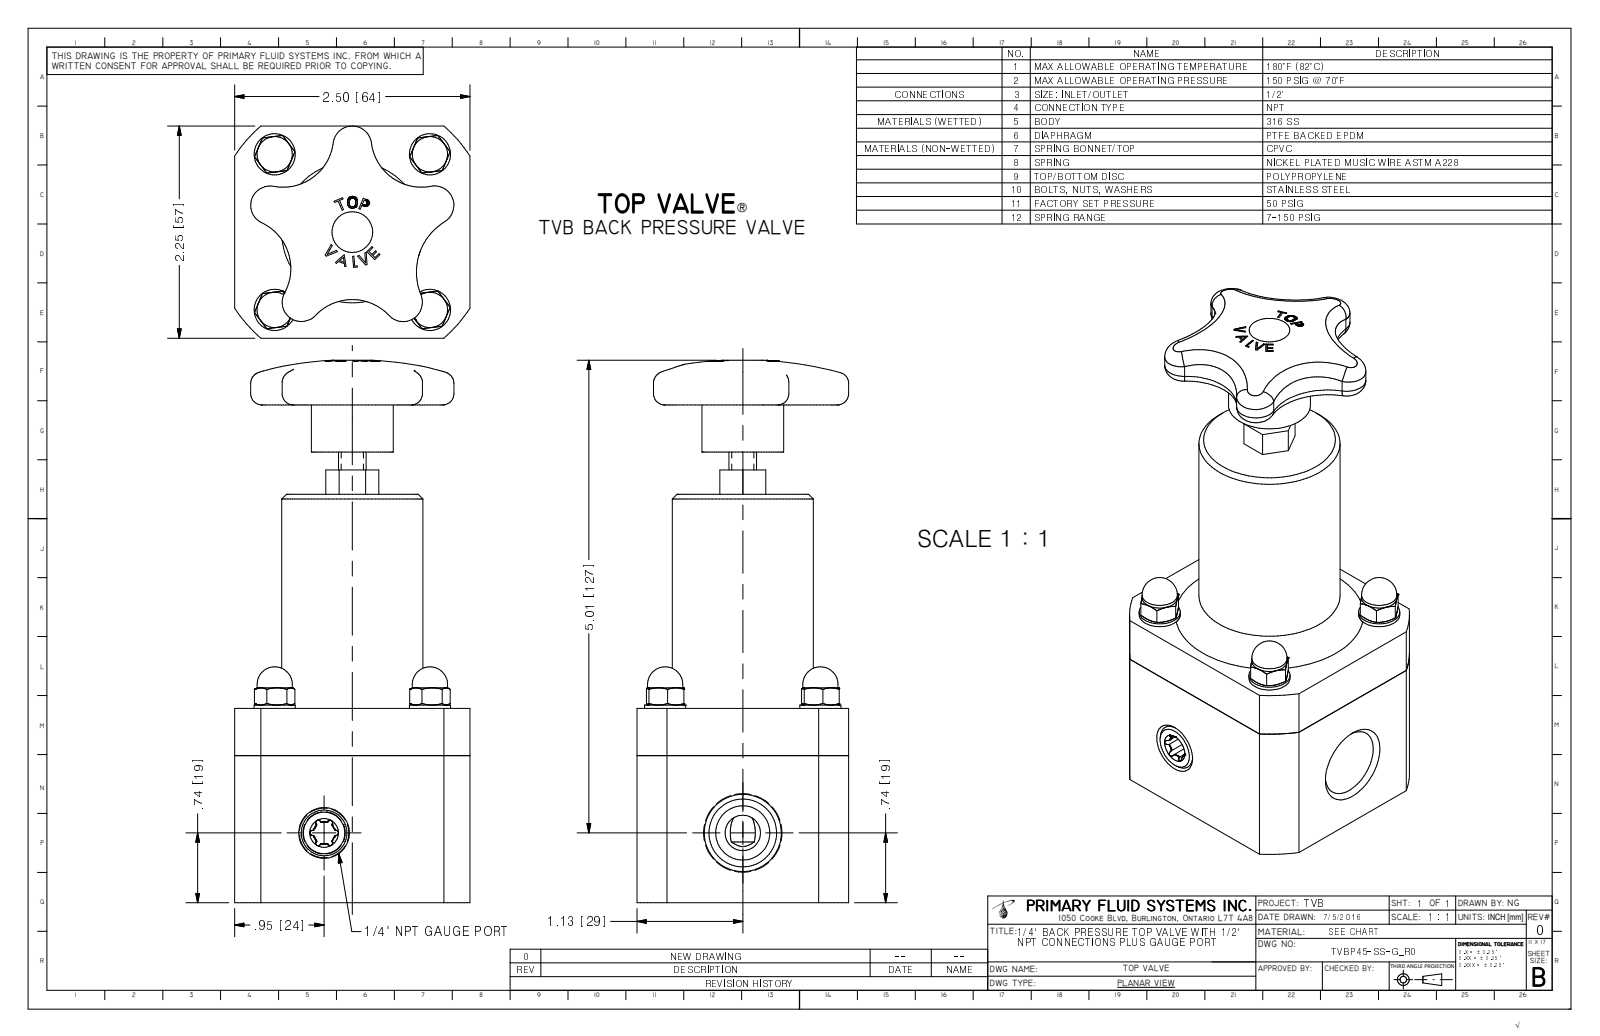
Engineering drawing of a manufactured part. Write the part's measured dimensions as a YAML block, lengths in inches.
part_name: "TVBP45-SS-G-R0"
step_written_by: "Autodesk Inventor 2009 (AUTOMOTIVE_DESIGN)"
units: inches
bodies: {solids: 1, faces: 359, planar: 148, cylindrical: 51, other: 160}
overall_size: [5.752, 2.5, 2.25]
volume: 16.16
surface_area: 56.44
round_holes:
  - {diameter: 0.147, count: 4}
  - {diameter: 0.719, count: 1}
round_bosses_or_shafts:
  - {diameter: 0.437, count: 4}
  - {diameter: 0.375, count: 4}
  - {diameter: 0.312, count: 4}
  - {diameter: 1.5, count: 1}
  - {diameter: 0.87, count: 1}
  - {diameter: 0.293, count: 1}
partial_cylinders:
  - {radius: 0.027, count: 6}
  - {radius: 0.085, count: 5}
  - {radius: 0.205, count: 5}
  - {radius: 0.536, count: 4}
  - {radius: 0.656, count: 4}
  - {radius: 0.625, count: 1}
  - {radius: 0.745, count: 1}
  - {radius: 1.488, count: 1}
face_to_face_distances: [2.25, 2.5, 2.06, 4.33, 2.27, 0.6, 1.9, 4.778, 2.718, 0.448]
hole_center_spacings: [1.65, 1.65, 2.334]
